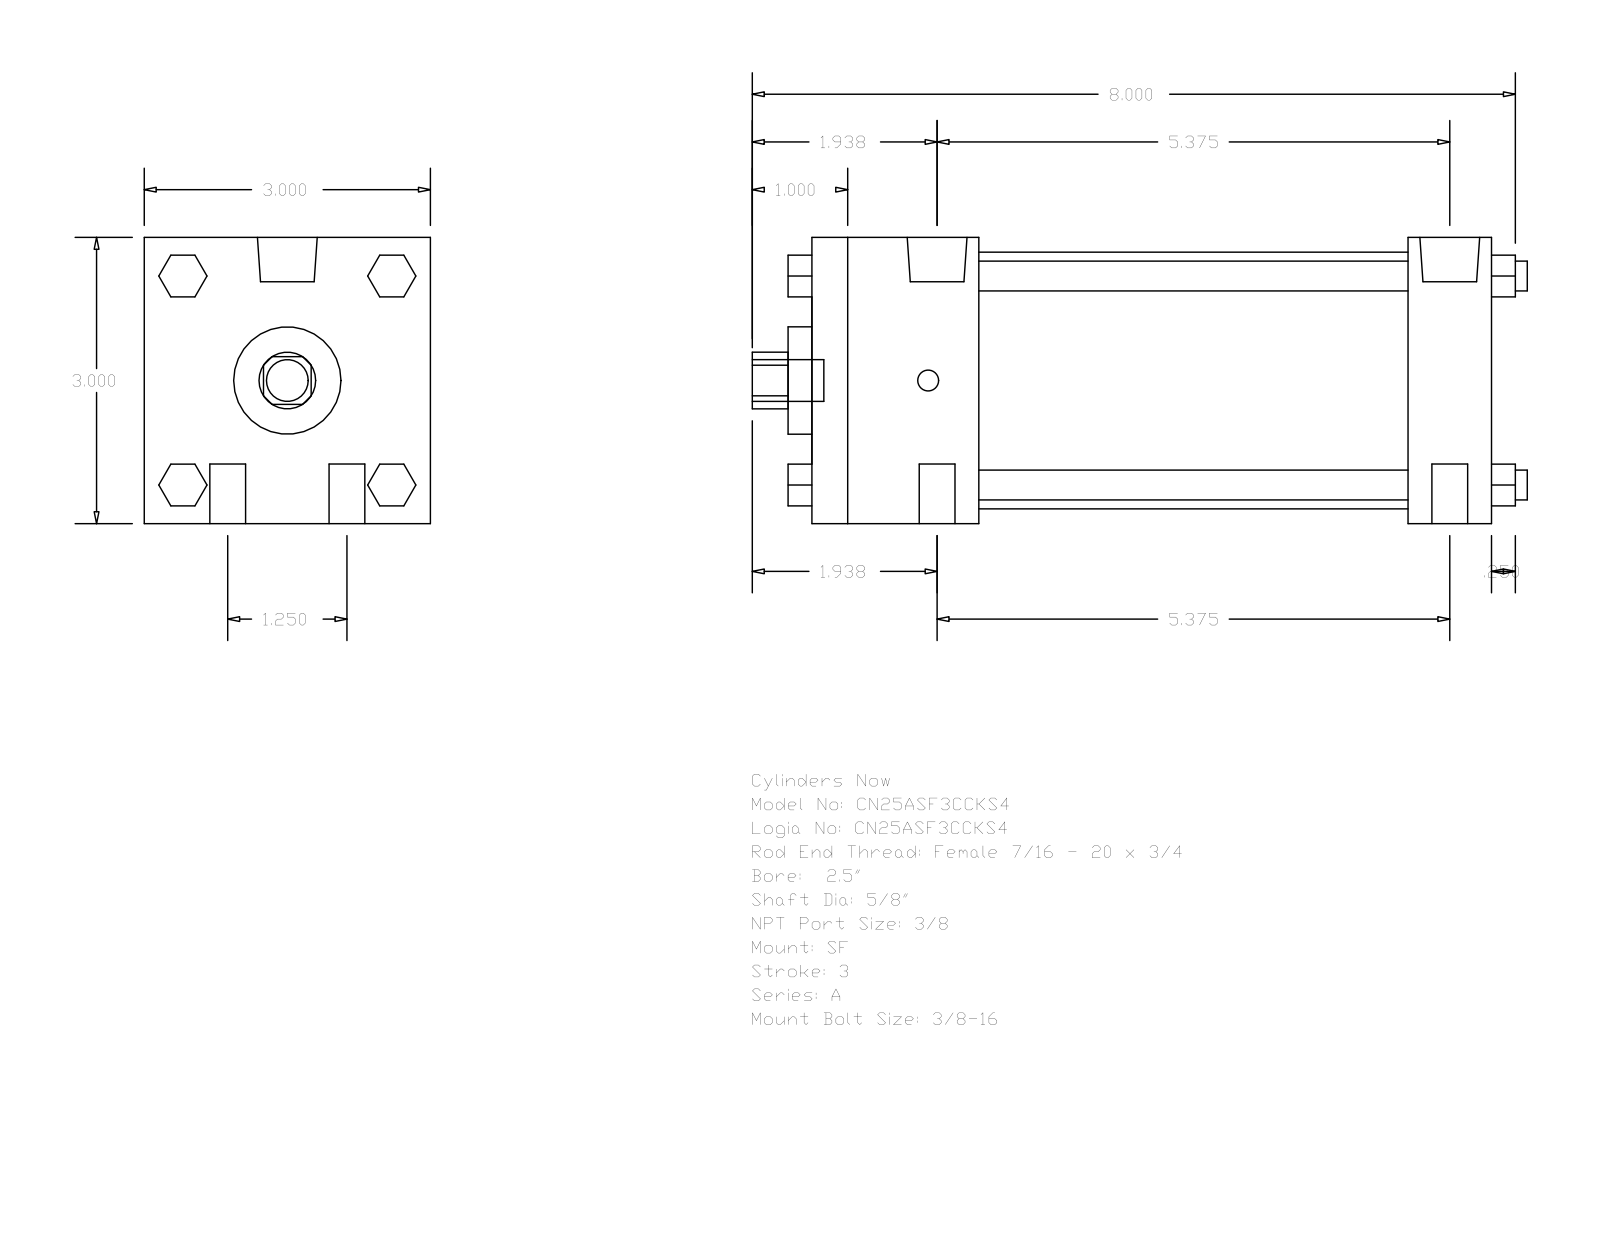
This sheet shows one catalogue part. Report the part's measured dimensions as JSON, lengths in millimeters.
{"part_name": "A_SF__0250_0.625", "step_written_by": "GSSL Pune (CONFIG_CONTROL_DESIGN)", "units": "millimeters", "bodies": {"solids": 0, "faces": 124, "planar": 94, "cylindrical": 30, "other": 0}, "overall_size": [206.38, 76.2, 76.2], "round_holes": [[15.88, 1], [28.57, 1], [68.33, 1]], "round_bosses_or_shafts": [[9.53, 4], [7.94, 4], [15.93, 2], [5.56, 2], [11.11, 1]], "partial_cylinders_radius": [[7.54, 1]], "face_to_face_distances": [76.2, 180.97, 44.45, 158.74, 22.23, 114.29, 136.52, 6.35, 187.32, 50.8]}
